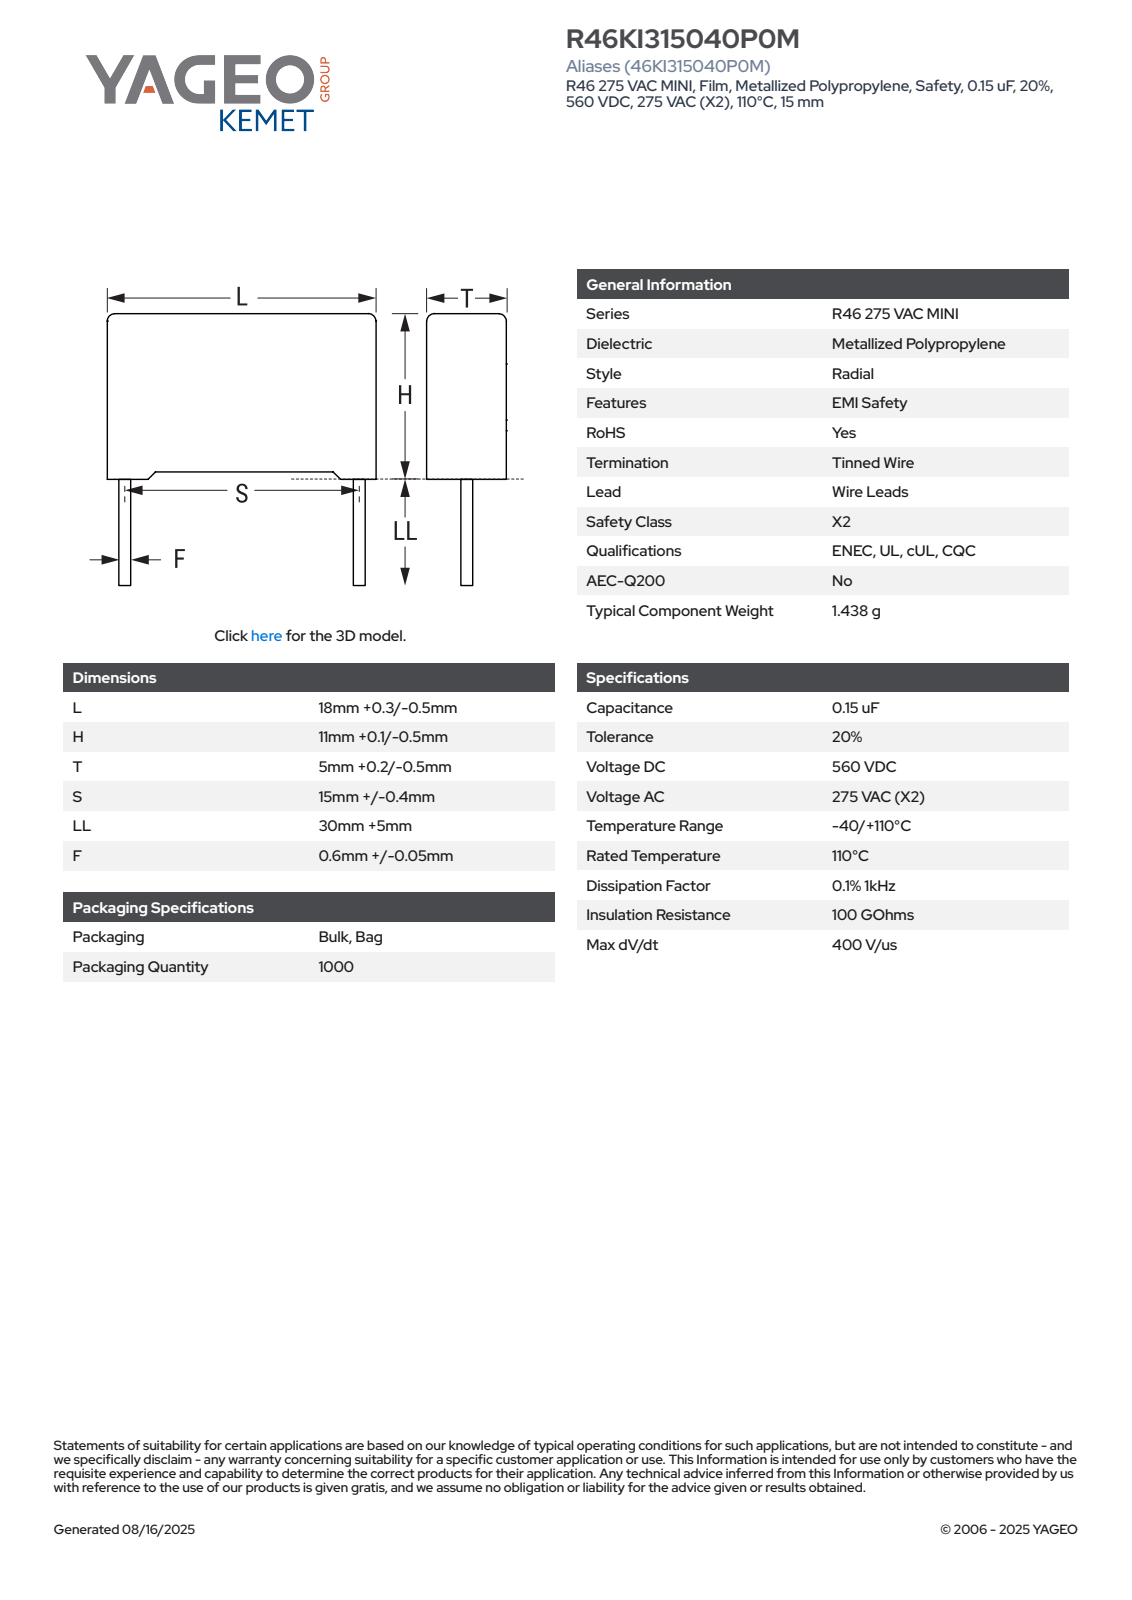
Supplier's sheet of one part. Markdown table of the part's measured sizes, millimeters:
| quantity | value |
| --- | --- |
| part name | CFR_RB2_18X11X5_L18.3H11.1T5.2S15LL35F0.65 |
| STEP written by | SolidWorks 2021 (AUTOMOTIVE_DESIGN) |
| units | millimeters |
| bodies | 4 solids, 85 faces (77 planar, 8 cylindrical, 0 other) |
| overall size | 46.1 × 18.3 × 5.21 |
| volume | 1 021 mm³ |
| surface area | 887 mm² |
| round bosses / shafts (diameter × count) | 0.65 × 2 |
| partial cylindrical surfaces (radius × count) | 0.5 × 4 |
| main face-to-face distances | 5.2, 10.35, 18.3, 0.61, 4.59, 0.37, 10.72, 0.38, 0.75, 11.1 |
